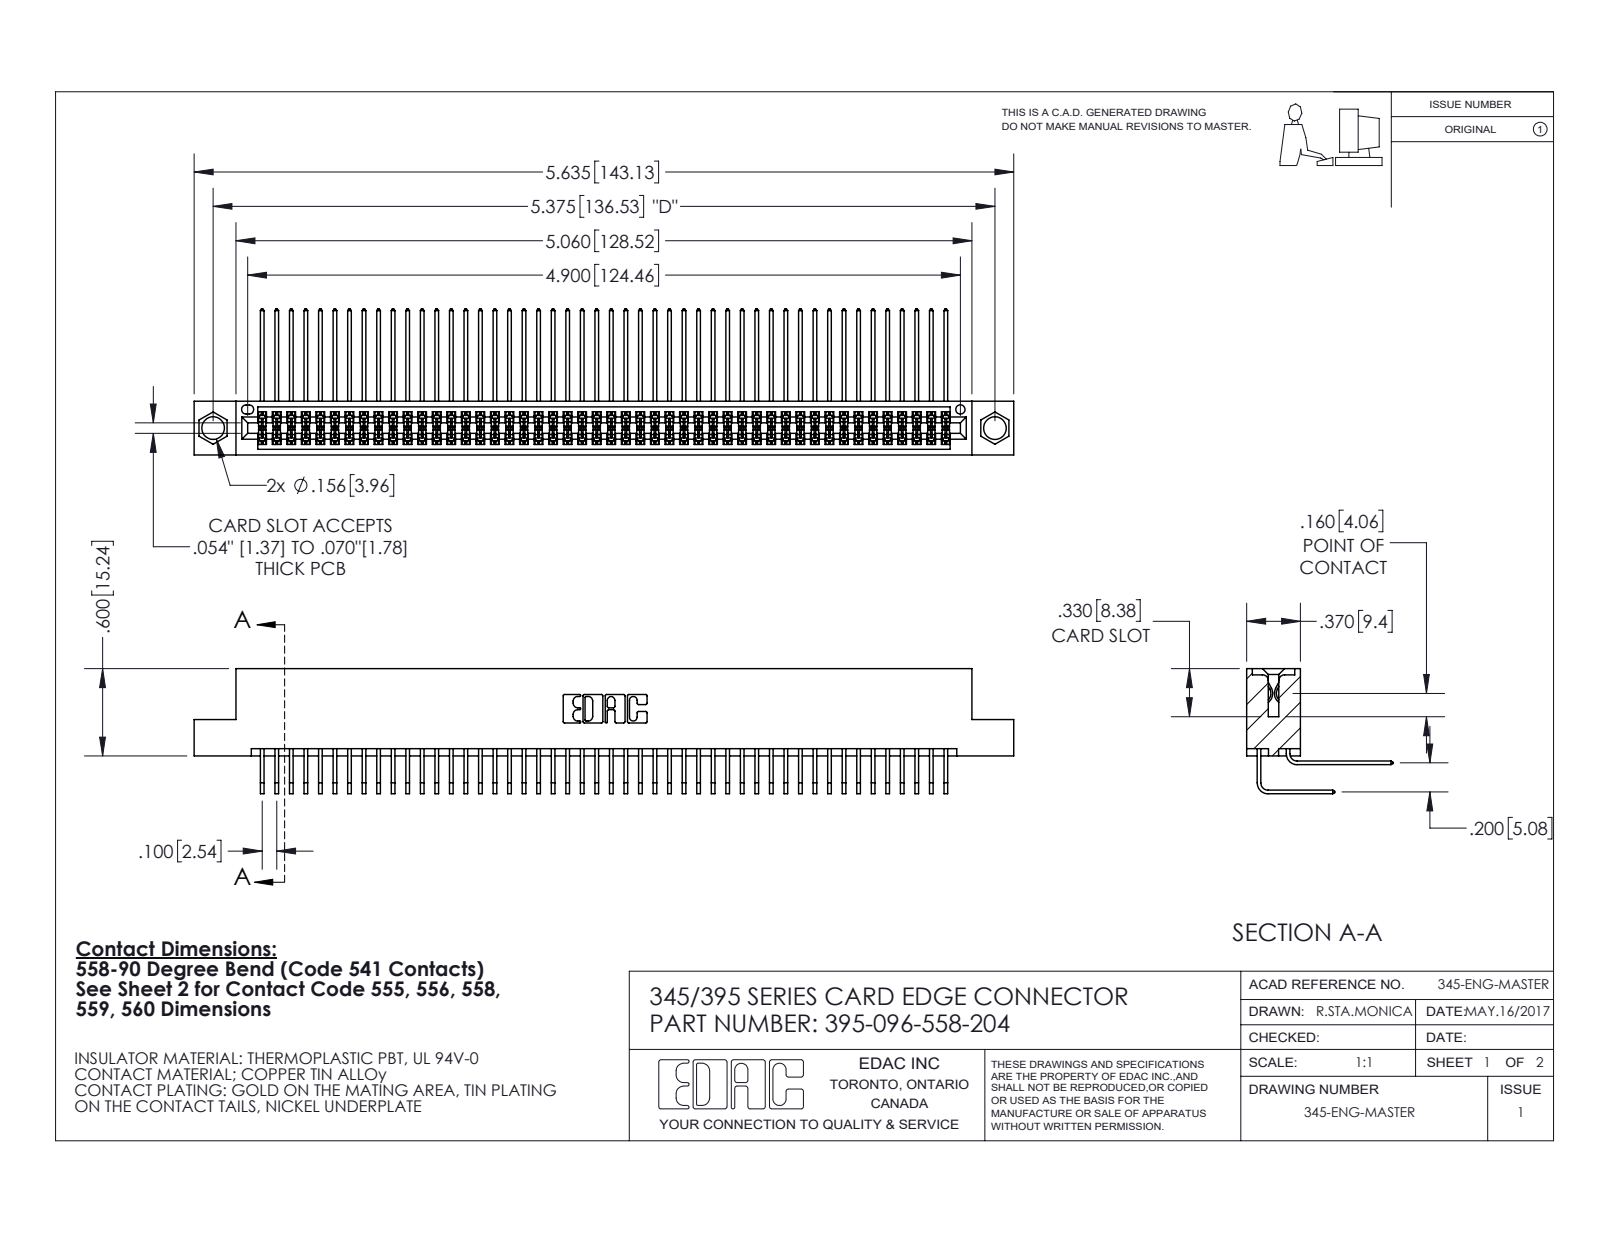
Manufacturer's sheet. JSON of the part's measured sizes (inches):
{"part_name": "345 Part_Flush Mounting Lugs - 0.156 Dia-TI; 345-292-001_558 559 Tail - 1; 395-096-558-204; 345-292-001_558 Tail - 2", "step_written_by": "SolidWorks 2020 (CONFIG_CONTROL_DESIGN)", "units": "inches", "bodies": {"solids": 97, "faces": 5132, "planar": 3454, "cylindrical": 1678, "other": 0}, "overall_size": [5.635, 1.005, 0.859], "volume_in3": 0.879, "surface_area_in2": 37, "round_holes": [[0.156, 2], [0.064, 1]], "partial_cylinders_radius": [[0.006, 192], [0.01, 22], [0.007, 6], [0.031, 6], [0.026, 3], [0.014, 2], [0.019, 2], [0.022, 2]], "face_to_face_distances": [0.072, 0.298, 0.2, 0.37, 0.098, 0.272, 0.025, 0.225, 0.025, 0.175], "hole_center_spacings": [0.27, 5.139, 5.375]}
